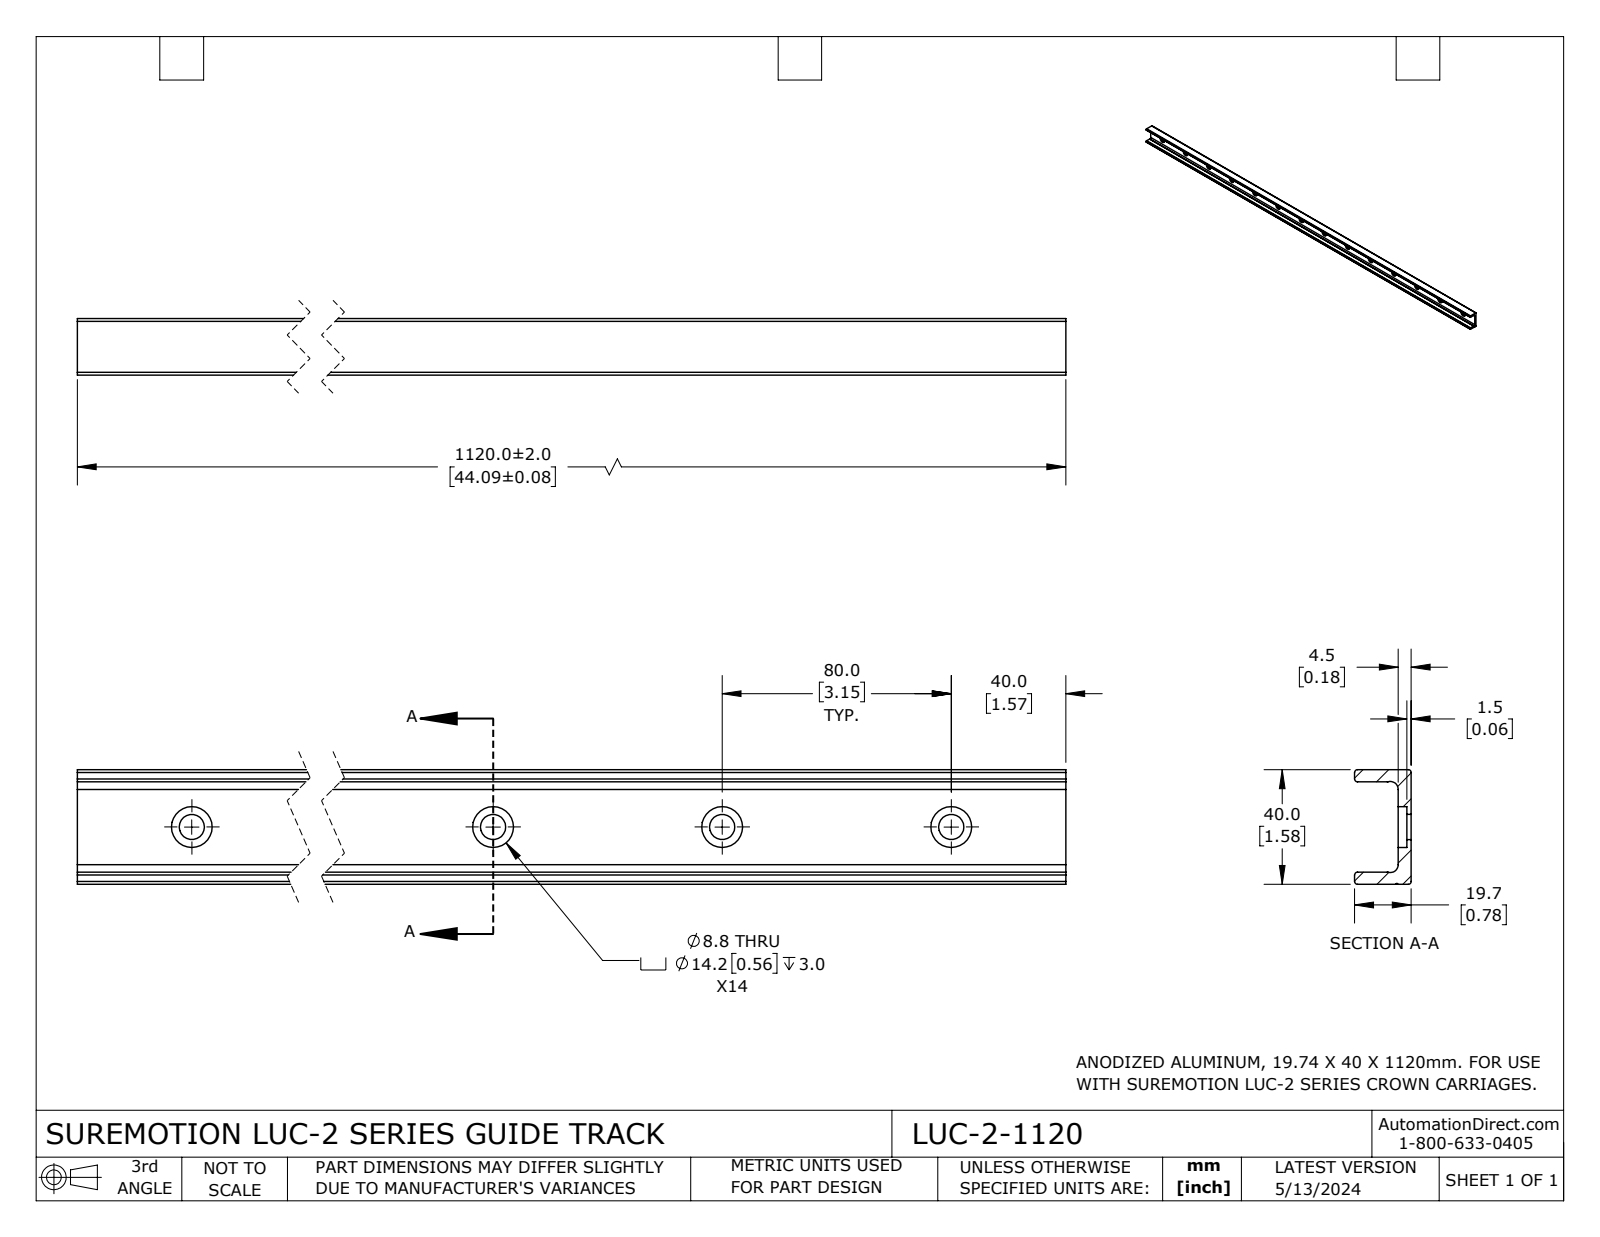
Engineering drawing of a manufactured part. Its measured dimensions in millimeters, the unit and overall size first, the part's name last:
Units: millimetres
Overall size (bounding box): 1120 × 40.01 × 19.74
Round holes (diameter × count): ⌀8.81 ×14, ⌀14.25 ×14
Partial cylindrical surfaces — rounded edges, fillets, slot ends (radius × count): R0.99 ×8, R2.77 ×2, R0.33 ×1
Main face-to-face distances: 4.5, 4.26, 35.76, 40.02, 31.5, 19.74, 15.24, 1.5, 3, 18.24
Hole centre spacings: 80, 160, 240, 320, 400, 480, 560, 640
Volume: 339 873 mm³ · Surface area: 164 622 mm²
Bodies: 1 solid, 92 faces (25 planar, 67 cylindrical, 0 other)
Part name (STEP PRODUCT): LUC-2-1120
STEP written by: SolidWorks 2023 (CONFIG_CONTROL_DESIGN)
